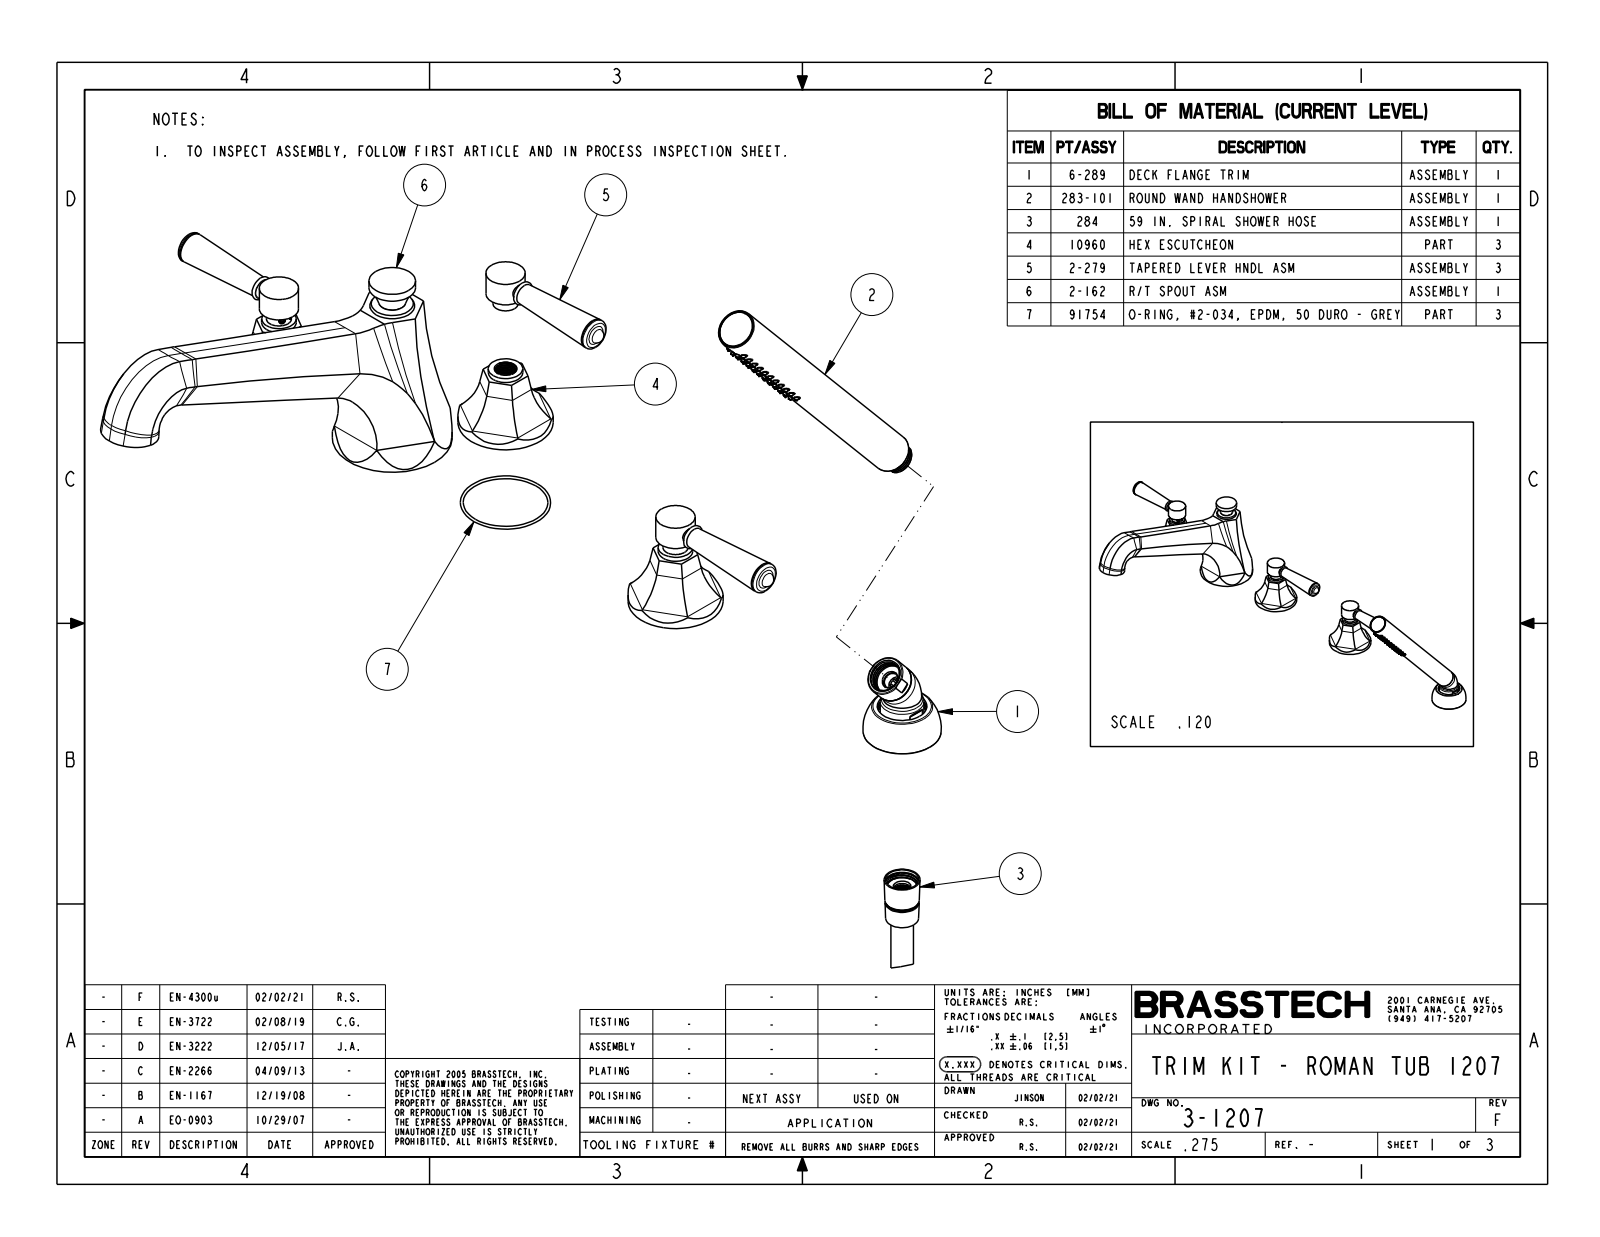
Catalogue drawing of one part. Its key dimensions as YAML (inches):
part_name: "3-1207"
step_written_by: "CREO PARAMETRIC BY PTC INC, 2019352 (CONFIG_CONTROL_DESIGN)"
units: inches
bodies: {solids: 6, faces: 685, planar: 135, cylindrical: 212, other: 338}
overall_size: [26.388, 11.484, 6.854]
volume: 57.41
surface_area: 205.9
round_holes:
  - {diameter: 0.046, count: 52}
  - {diameter: 0.235, count: 1}
  - {diameter: 0.49, count: 1}
  - {diameter: 0.87, count: 1}
  - {diameter: 1.22, count: 1}
  - {diameter: 1.61, count: 1}
round_bosses_or_shafts:
  - {diameter: 0.98, count: 4}
  - {diameter: 2.375, count: 3}
  - {diameter: 0.86, count: 3}
  - {diameter: 0.625, count: 3}
  - {diameter: 2.99, count: 1}
  - {diameter: 1.823, count: 1}
  - {diameter: 1.65, count: 1}
  - {diameter: 1.26, count: 1}
partial_cylinders:
  - {radius: 1.541, count: 18}
  - {radius: 0.05, count: 6}
  - {radius: 13, count: 6}
  - {radius: 2.75, count: 1}
face_to_face_distances: [1.957, 3.928, 6.874, 2.946, 4.115, 2.158, 1.527, 0.43, 2.588, 1.647]
hole_center_spacings: [0.512, 0.335, 0.187, 0.512, 0.535, 0.367, 0.685, 0.812]
